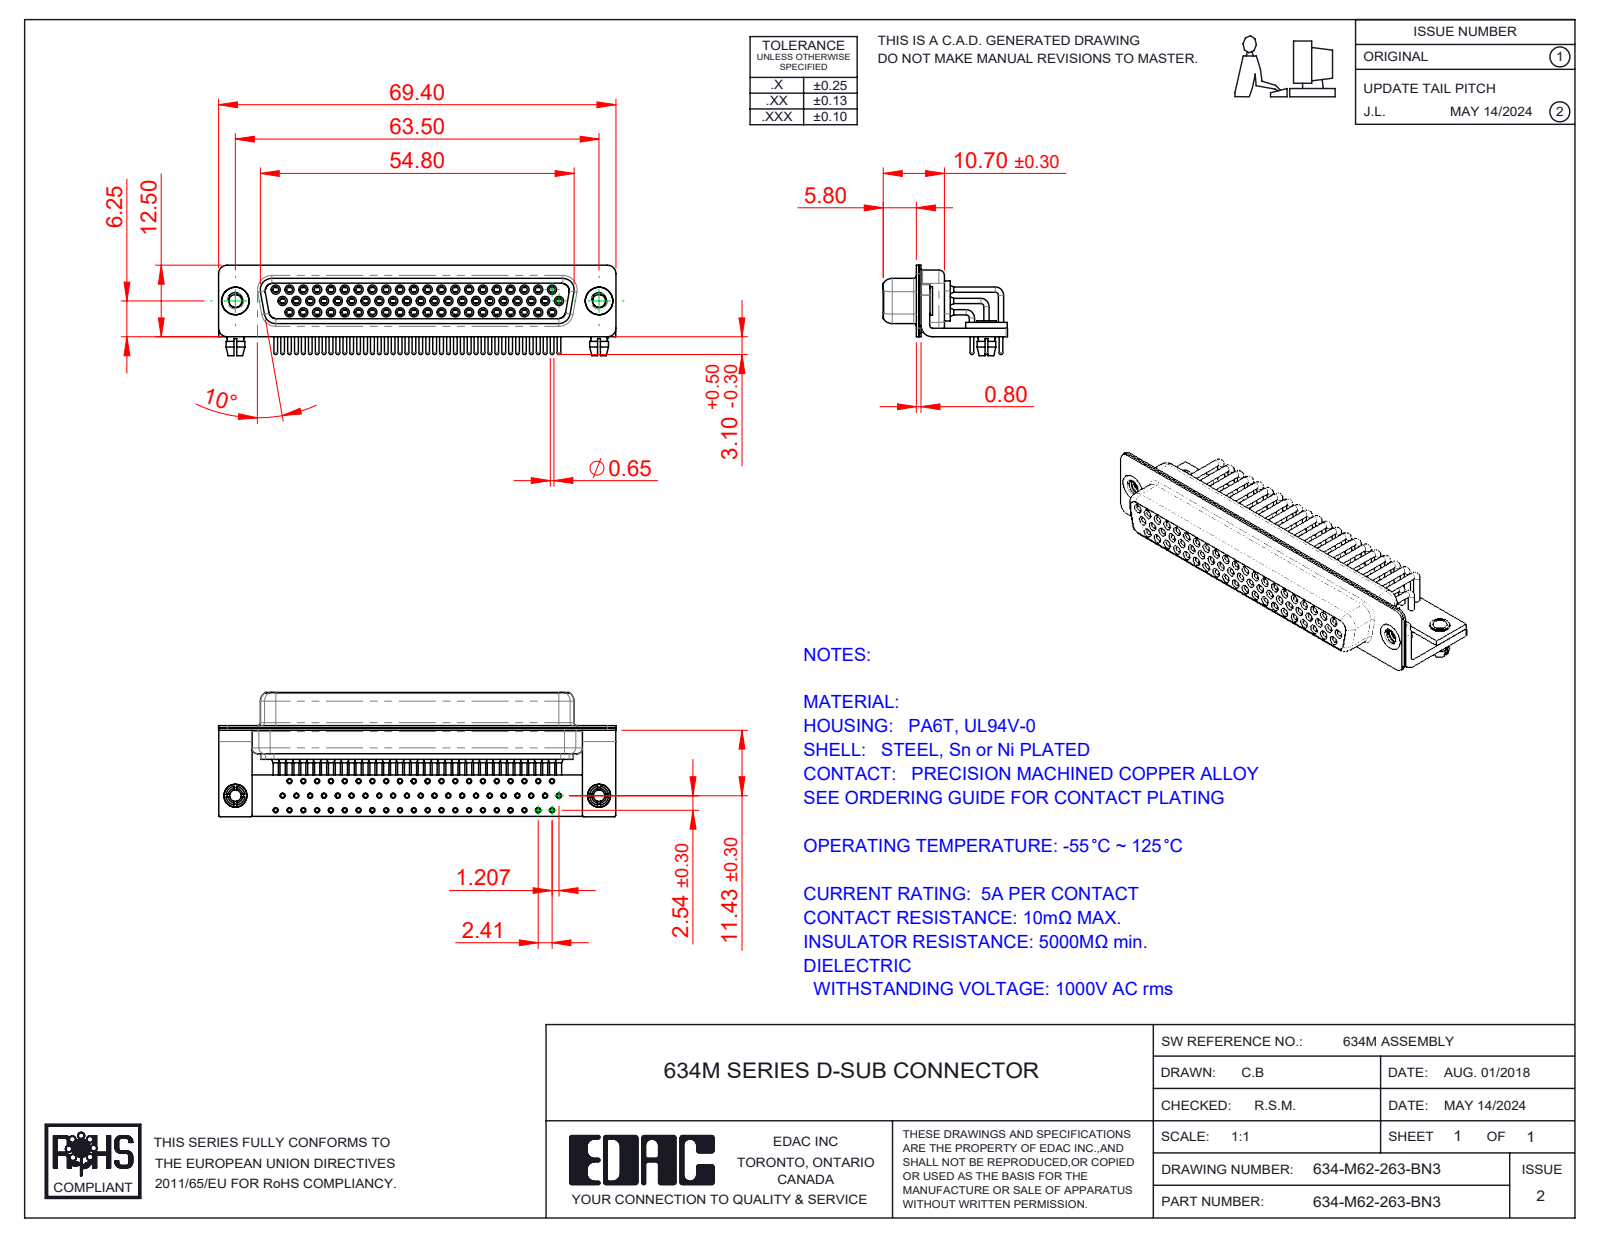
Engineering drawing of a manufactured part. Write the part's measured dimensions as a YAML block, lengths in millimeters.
part_name: "634M Contact Row 3; 634M Shell Front_62 Contacts; 634M Stabilizer Board_62 Contacts; 634M Housing_62 Contacts (+7 more)"
step_written_by: "SolidWorks 2016 (CONFIG_CONTROL_DESIGN)"
units: millimeters
bodies: {solids: 72, faces: 3831, planar: 1071, cylindrical: 1741, other: 1019}
overall_size: [69.4, 21.7, 15.8]
volume: 6178
surface_area: 19963
round_holes:
  - {diameter: 2, count: 64}
  - {diameter: 0.9, count: 62}
  - {diameter: 1, count: 62}
  - {diameter: 1.1, count: 62}
  - {diameter: 1.7, count: 62}
  - {diameter: 1.8, count: 62}
  - {diameter: 2.26, count: 2}
  - {diameter: 2.5, count: 2}
  - {diameter: 3.2, count: 2}
  - {diameter: 4, count: 2}
  - {diameter: 4.8, count: 2}
round_bosses_or_shafts:
  - {diameter: 0.9, count: 118}
  - {diameter: 1.6, count: 62}
  - {diameter: 1.5, count: 62}
  - {diameter: 0.65, count: 62}
  - {diameter: 2, count: 56}
  - {diameter: 5, count: 2}
  - {diameter: 4.9, count: 2}
  - {diameter: 4, count: 2}
partial_cylinders:
  - {radius: 0.25, count: 16}
  - {radius: 1.5, count: 16}
  - {radius: 2, count: 13}
  - {radius: 1.35, count: 8}
  - {radius: 1.6, count: 8}
  - {radius: 0.5, count: 5}
  - {radius: 0.6, count: 4}
  - {radius: 0.65, count: 4}
face_to_face_distances: [0.4, 2.3, 1, 1.9, 1.45, 8.95, 8.5, 0.85, 0.8, 9.35]
hole_center_spacings: [7.24, 2.41, 9.65, 4.83, 14.48, 16.89, 2.81, 2.32]
